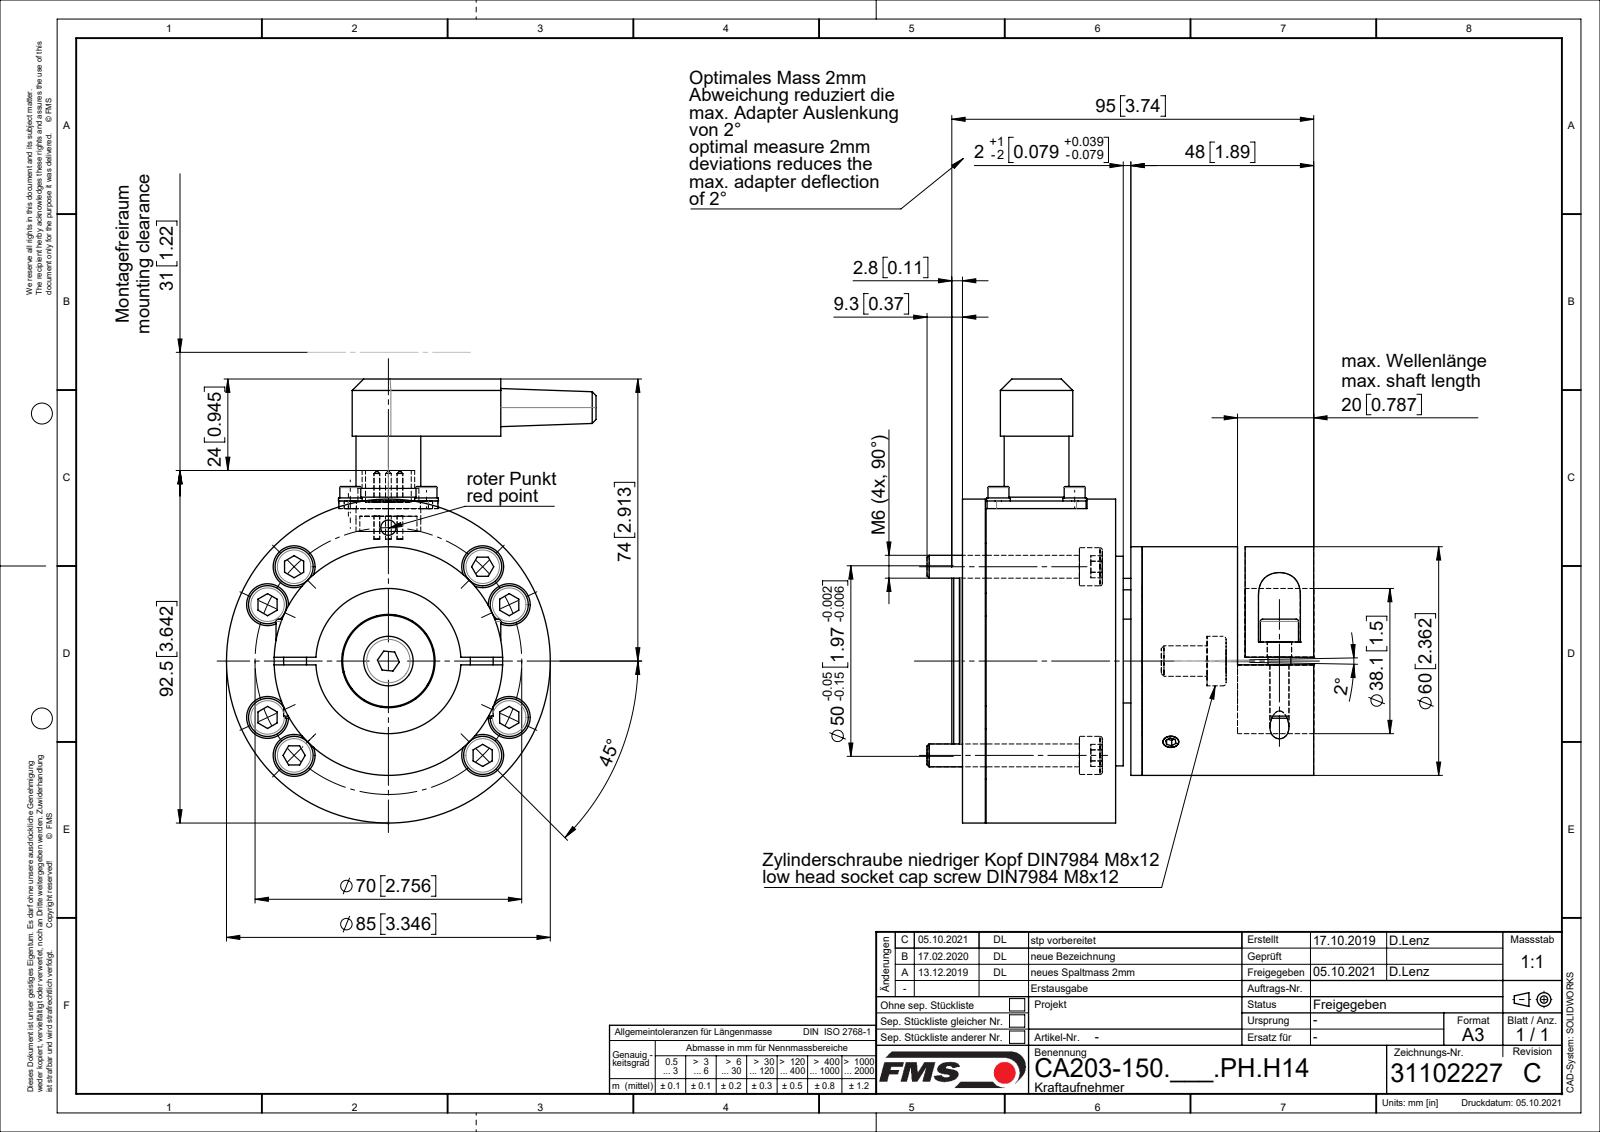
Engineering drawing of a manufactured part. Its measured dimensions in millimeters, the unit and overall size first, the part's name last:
Units: millimetres
Overall size (bounding box): 116.5 × 101.5 × 97
Round holes (diameter × count): ⌀2.5 ×8, ⌀6.5 ×8, ⌀11 ×8, ⌀5 ×6, ⌀2 ×5, ⌀4 ×5, ⌀3.1 ×4, ⌀3.2 ×4, ⌀3.6 ×4, ⌀7 ×4, ⌀6.4 ×2, ⌀3 ×1
Round bosses / shafts (diameter × count): ⌀6 ×11, ⌀10 ×10, ⌀3 ×8, ⌀1.5 ×5, ⌀6.2 ×4, ⌀5.7 ×4, ⌀5.5 ×4, ⌀85 ×1
Partial cylindrical surfaces — rounded edges, fillets, slot ends (radius × count): R2.5 ×4, R5 ×2, R5.5 ×2, R9.5 ×1
Main face-to-face distances: 2, 30, 41, 6, 10, 45, 3, 34, 15, 50
Hole centre spacings: 35, 20, 24.78, 25.2, 32.8, 51.14, 56.46, 6
Volume: 293 362 mm³ · Surface area: 111 548 mm²
Bodies: 44 solids, 839 faces (302 planar, 339 cylindrical, 198 other)
Part name (STEP PRODUCT): Sch DIN9021_M8; 31102204_01; Flanschstecker_M14x1_Mini_5pol; Gew-Sti-I6kt-Zapfen DIN915_M5x10 (+8 more)
STEP written by: SolidWorks 2018 (CONFIG_CONTROL_DESIGN)
